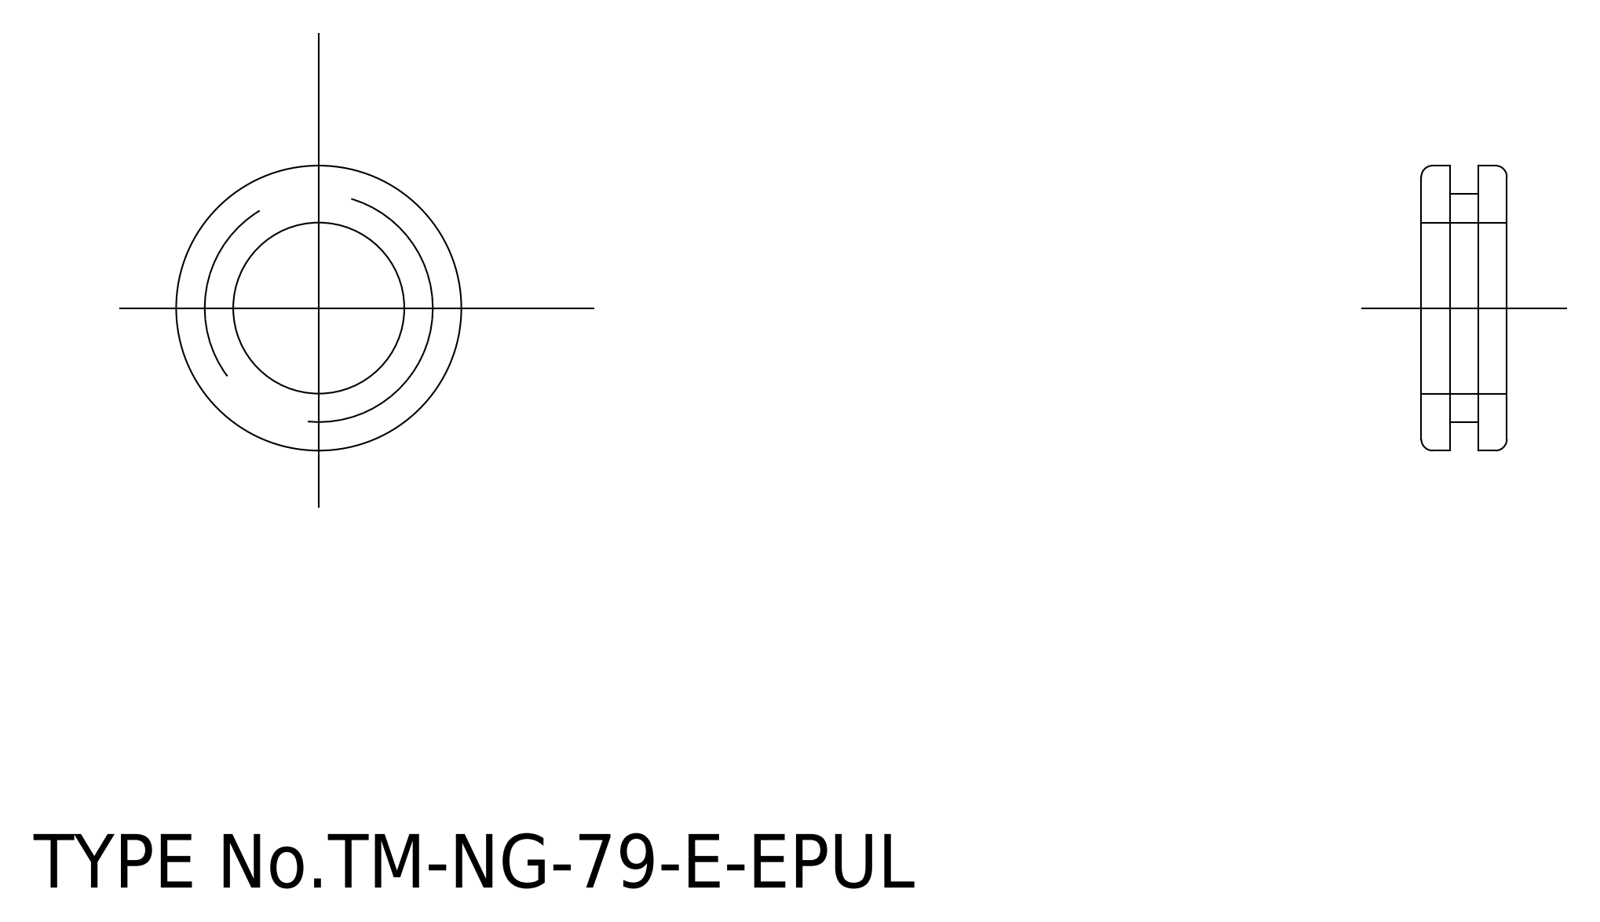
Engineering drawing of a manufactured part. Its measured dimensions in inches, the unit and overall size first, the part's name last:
Units: inches
Overall size (bounding box): 0.591 × 0.591 × 0.177
Round holes (diameter × count): ⌀0.354 ×1
Round bosses / shafts (diameter × count): ⌀0.591 ×1, ⌀0.472 ×1
Main face-to-face distances: 0.059, 0.118, 0.177
Volume: 0.025 in³ · Surface area: 1.01 in²
Bodies: 1 solid, 16 faces (4 planar, 8 cylindrical, 4 other)
STEP written by: spGate 15.6.1 (AUTOMOTIVE_DESIGN)
